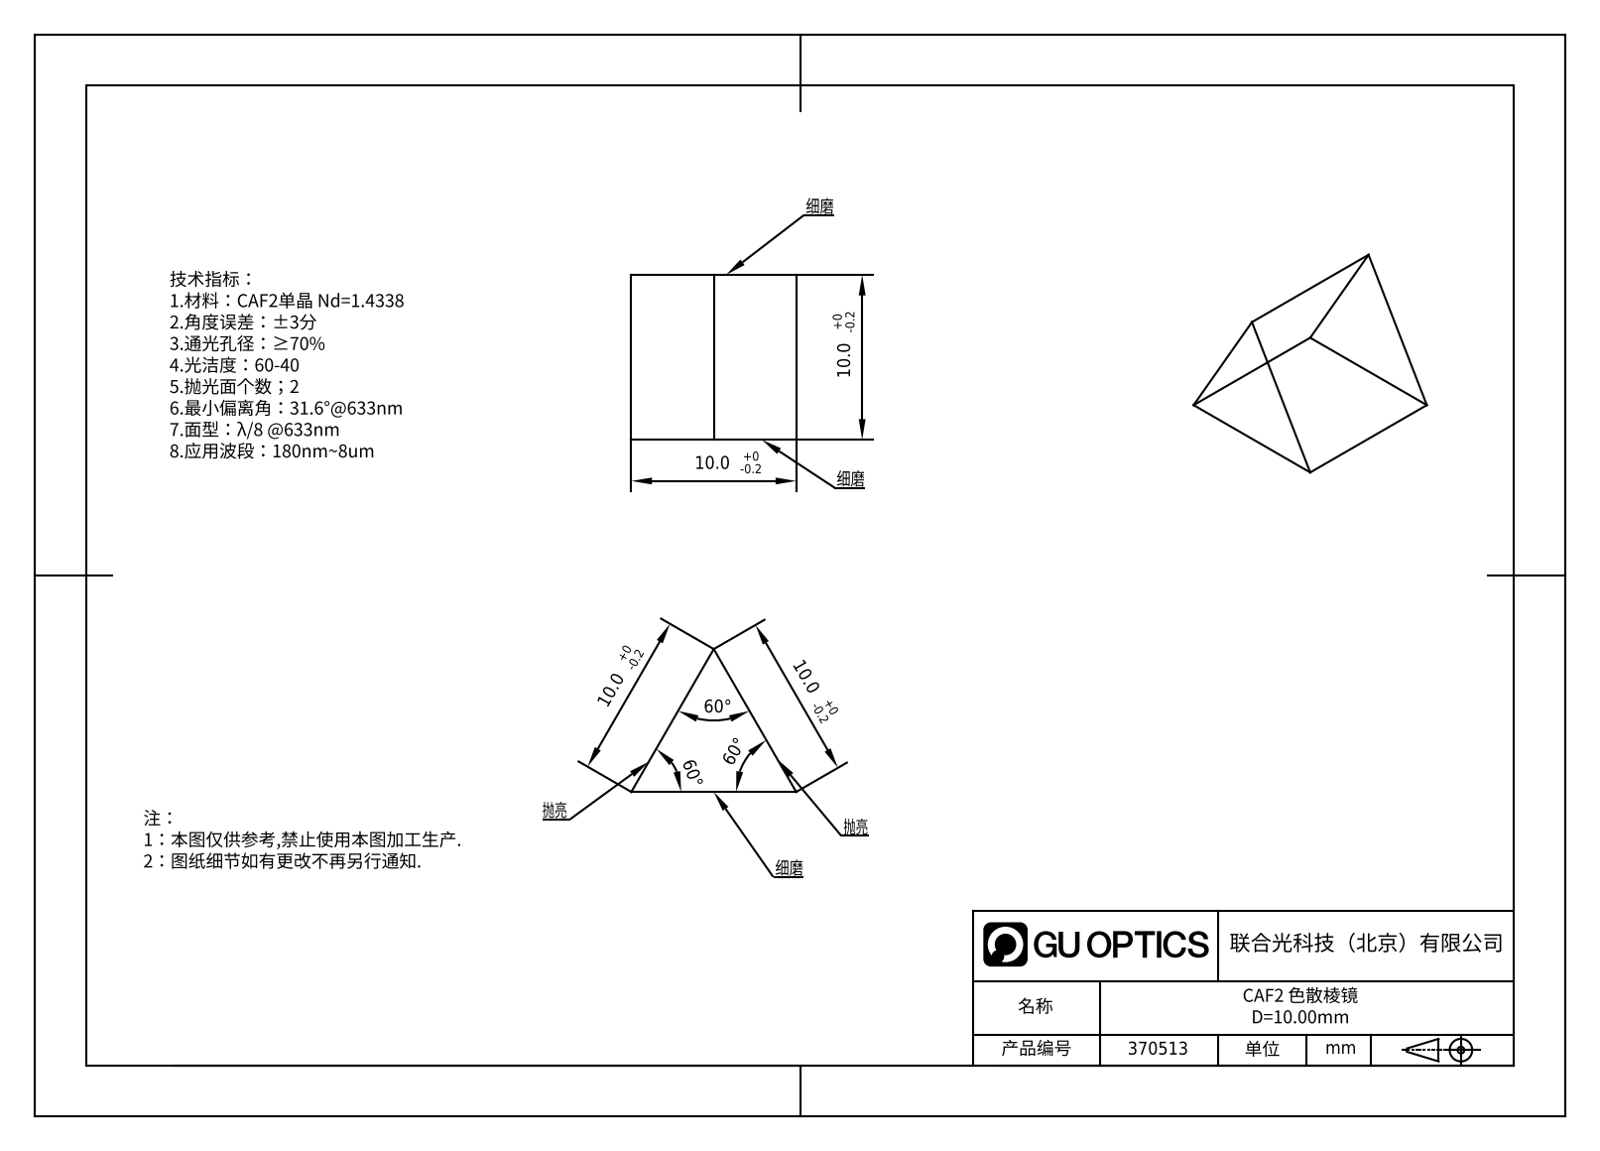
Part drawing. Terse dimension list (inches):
name: GPD-010-C
written by: SolidWorks 2022 (AUTOMOTIVE_DESIGN)
unit: in
bodies: 1 solid, 20 faces (20 planar, 0 cylindrical, 0 other)
size: 0.394 × 0.39 × 0.339
volume: 0.026 in³; area: 0.591 in²
face distances: 0.394
